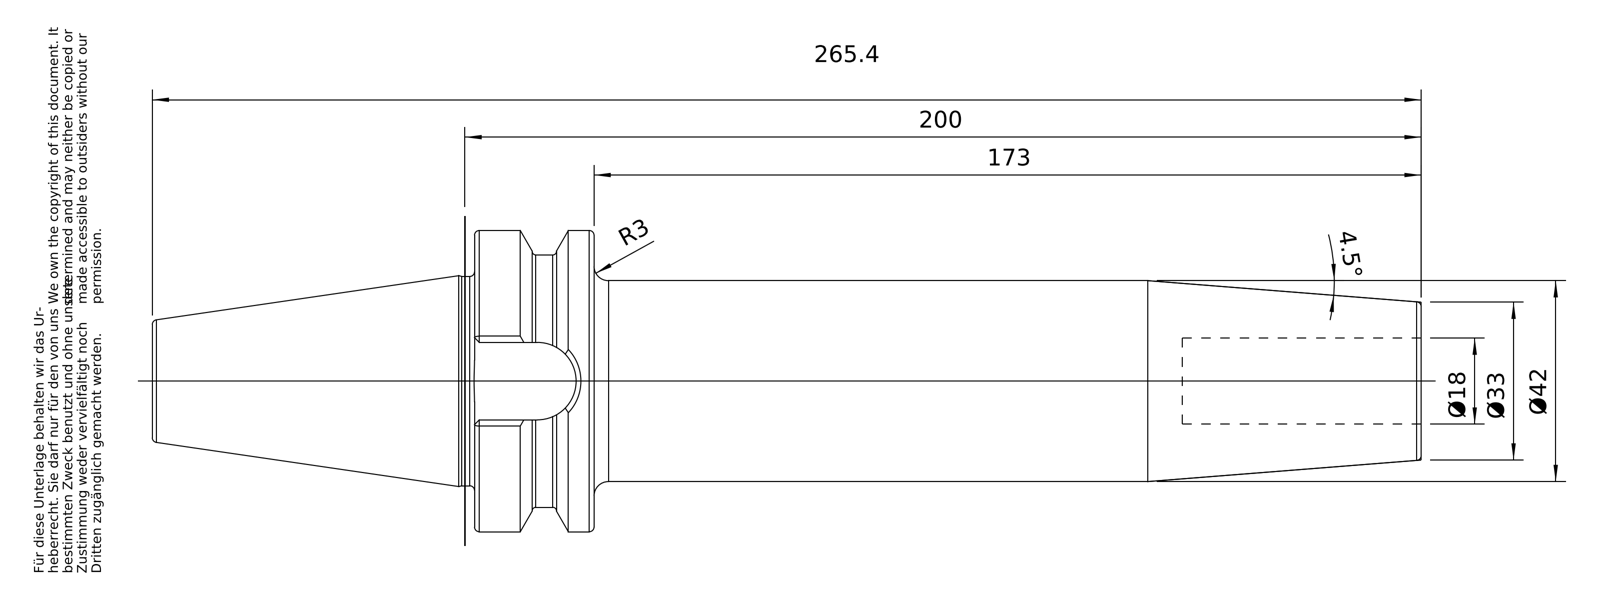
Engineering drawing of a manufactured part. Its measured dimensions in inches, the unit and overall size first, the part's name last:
Units: inches
Overall size (bounding box): 10.449 × 2.48 × 2.48
Round holes (diameter × count): ⌀0.545 ×1, ⌀0.67 ×1, ⌀0.689 ×1, ⌀0.709 ×1
Round bosses / shafts (diameter × count): ⌀2.48 ×1, ⌀2.077 ×1, ⌀1.722 ×1, ⌀1.654 ×1, ⌀0.63 ×1
Partial cylindrical surfaces — rounded edges, fillets, slot ends (radius × count): R0.319 ×1
Main face-to-face distances: 0.984, 7.795, 6.811, 1.768, 5.827, 4.843, 1.969, 0.638, 2.654, 3.638
Volume: 20.6 in³ · Surface area: 71.25 in²
Bodies: 1 solid, 96 faces (26 planar, 22 cylindrical, 48 other)
Part name (STEP PRODUCT): 40-646-18
STEP written by: PRO/ENGINEER BY PARAMETRIC TECHNOLOGY CORPORATION, 2010430 (CONFIG_CONTROL_DESIGN)
